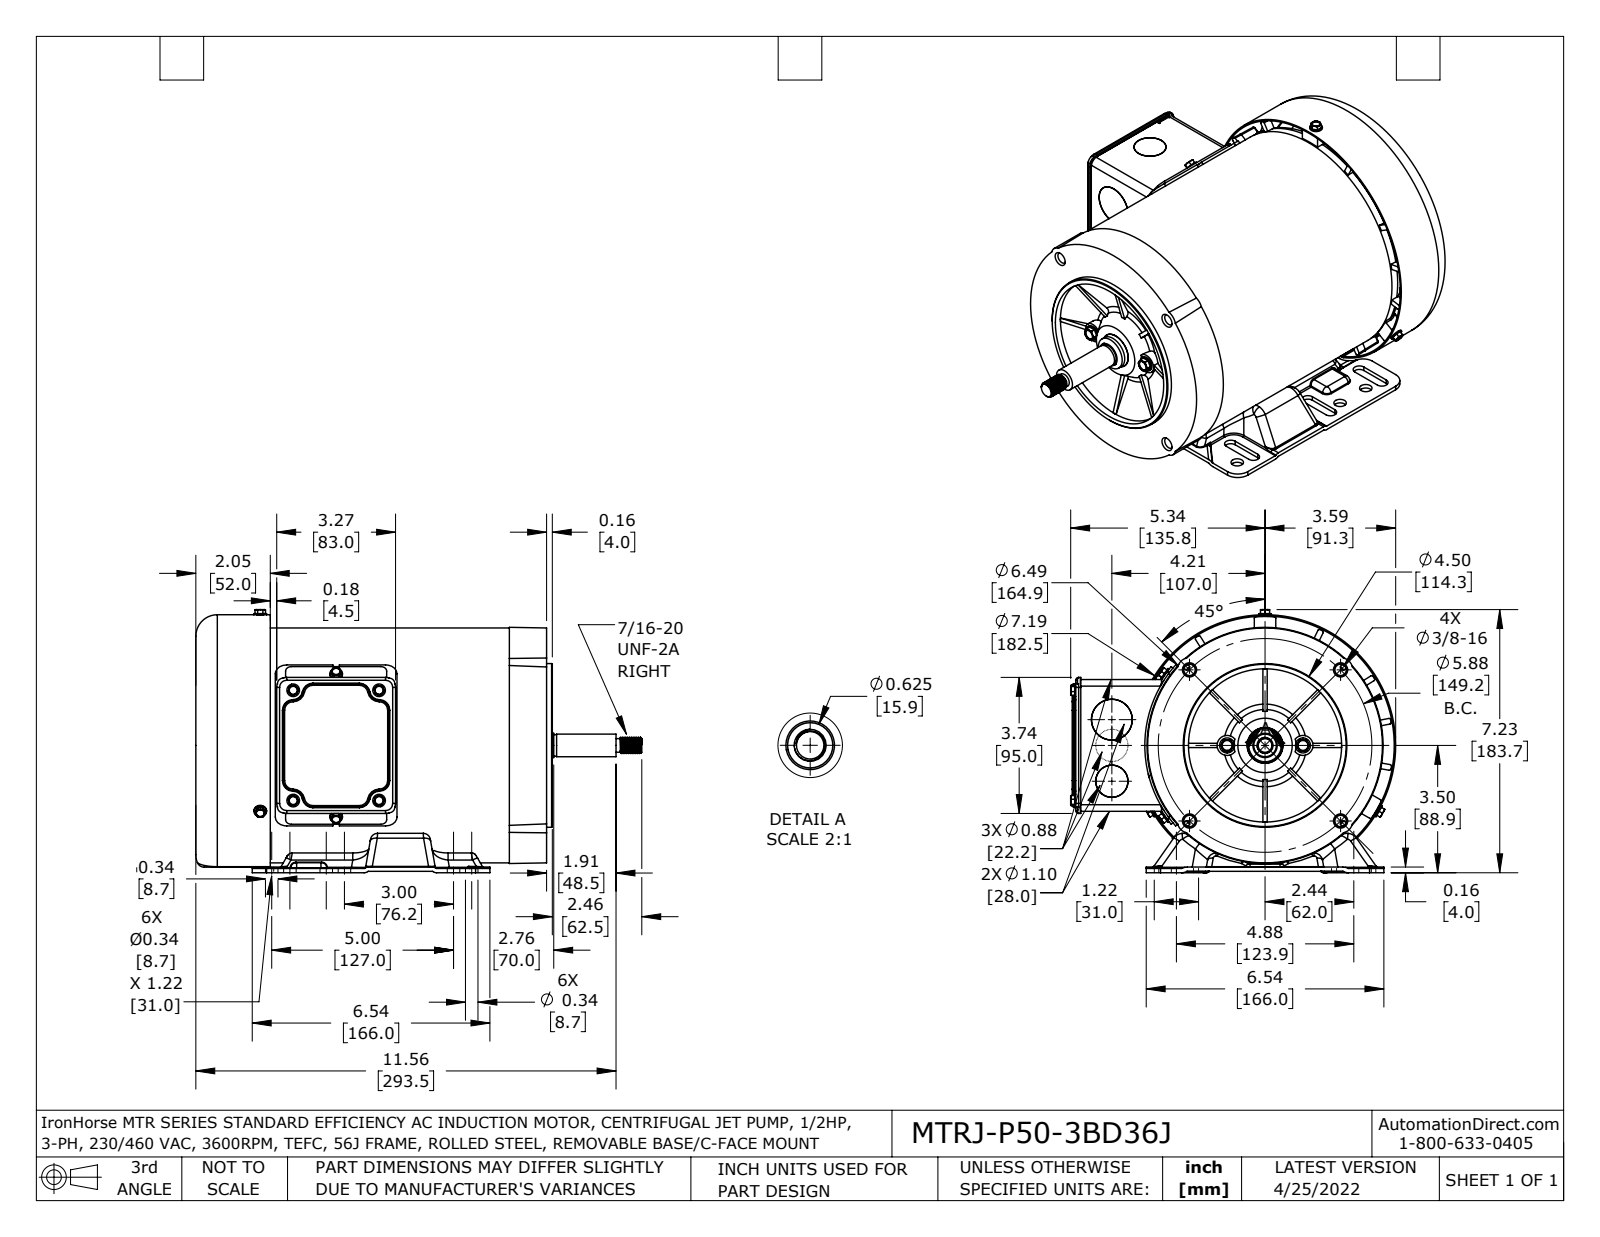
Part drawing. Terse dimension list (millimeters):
name: MTRJ-P50-3BD36J redcmb1 coord fxt
written by: SolidWorks 2021 (AUTOMOTIVE_DESIGN)
unit: mm
bodies: 29 solids, 2729 faces (658 planar, 899 cylindrical, 1172 other)
size: 311.5 × 227 × 183.7
volume: 757 900 mm³; area: 576 000 mm²
holes: 10× ⌀5, 9× ⌀5.6, 8× ⌀7, 7× ⌀3.5, 6× ⌀5.5, 6× ⌀8.3, 6× ⌀8.7, 4× ⌀3.8, 4× ⌀4.5, 4× ⌀8, 2× ⌀3.4, 2× ⌀6.9
bosses: 9× ⌀4.2, 8× ⌀8.8, 6× ⌀6, 2× ⌀10.5, 2× ⌀4.8, 1× ⌀182.5, 1× ⌀114.3, 1× ⌀24
rounds: 109× R3, 65× R1, 32× R4, 30× R0.5, 26× R3.5, 18× R2, 18× R7, 12× R4.4
face distances: 1, 3, 1.6, 4, 245, 244, 2, 90.4, 78.4, 1.2
hole spacings: 107.2, 77, 2.4, 58.9, 61.2, 74.6, 75.7, 95.2
